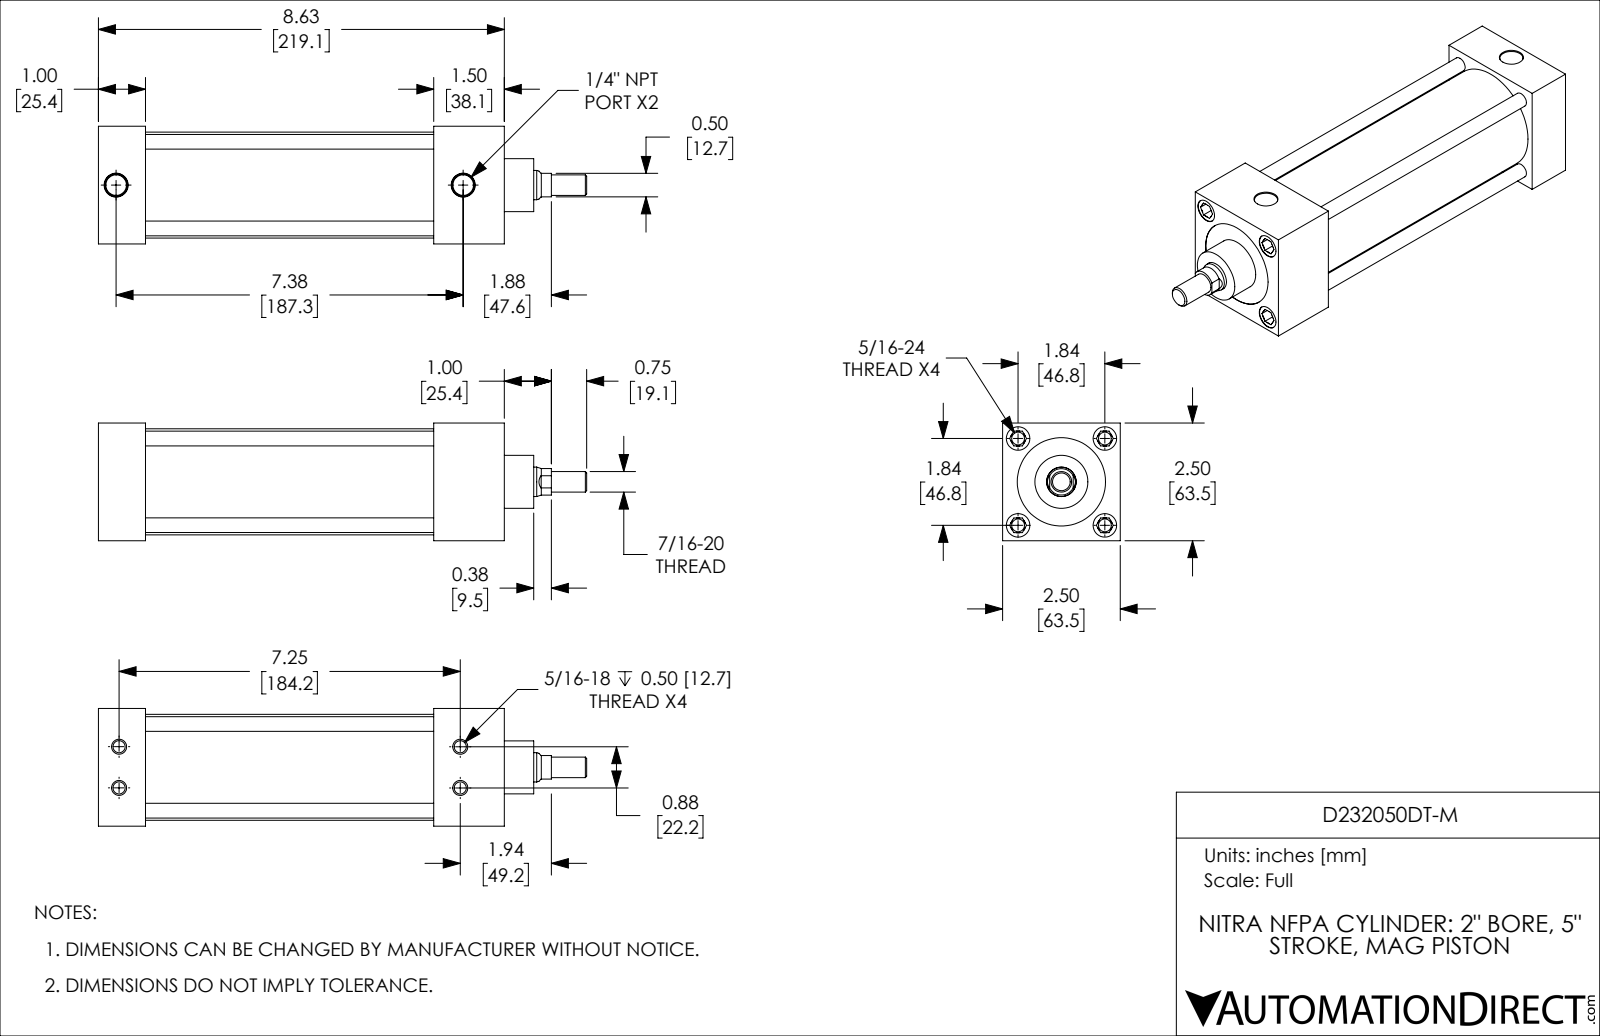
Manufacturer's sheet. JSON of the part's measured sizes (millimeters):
{"part_name": "D232050DT-M; D232050DT-M_PISTON_KK1; D232050DT-M_BODY", "step_written_by": "SolidWorks 2019 (CONFIG_CONTROL_DESIGN)", "units": "millimeters", "bodies": {"solids": 2, "faces": 200, "planar": 58, "cylindrical": 62, "other": 80}, "overall_size": [263.5, 63.5, 63.5], "volume_mm3": 453800, "surface_area_mm2": 127800, "round_holes": [[6.9, 7], [6.5, 4], [12.7, 4], [11.1, 2], [15.9, 1], [47.6, 1], [50.8, 1]], "round_bosses_or_shafts": [[7.9, 4], [57.2, 1], [50.8, 1], [28.6, 1], [15.8, 1], [11.1, 1]], "partial_cylinders_radius": [[7.1, 1]], "face_to_face_distances": [63.5, 25.4, 181, 155.6, 28.6, 54, 127, 38.1, 219.1, 193.7], "hole_center_spacings": [46.7, 46.8, 33, 11.2, 11.3, 22.2, 33.1, 66.1]}
